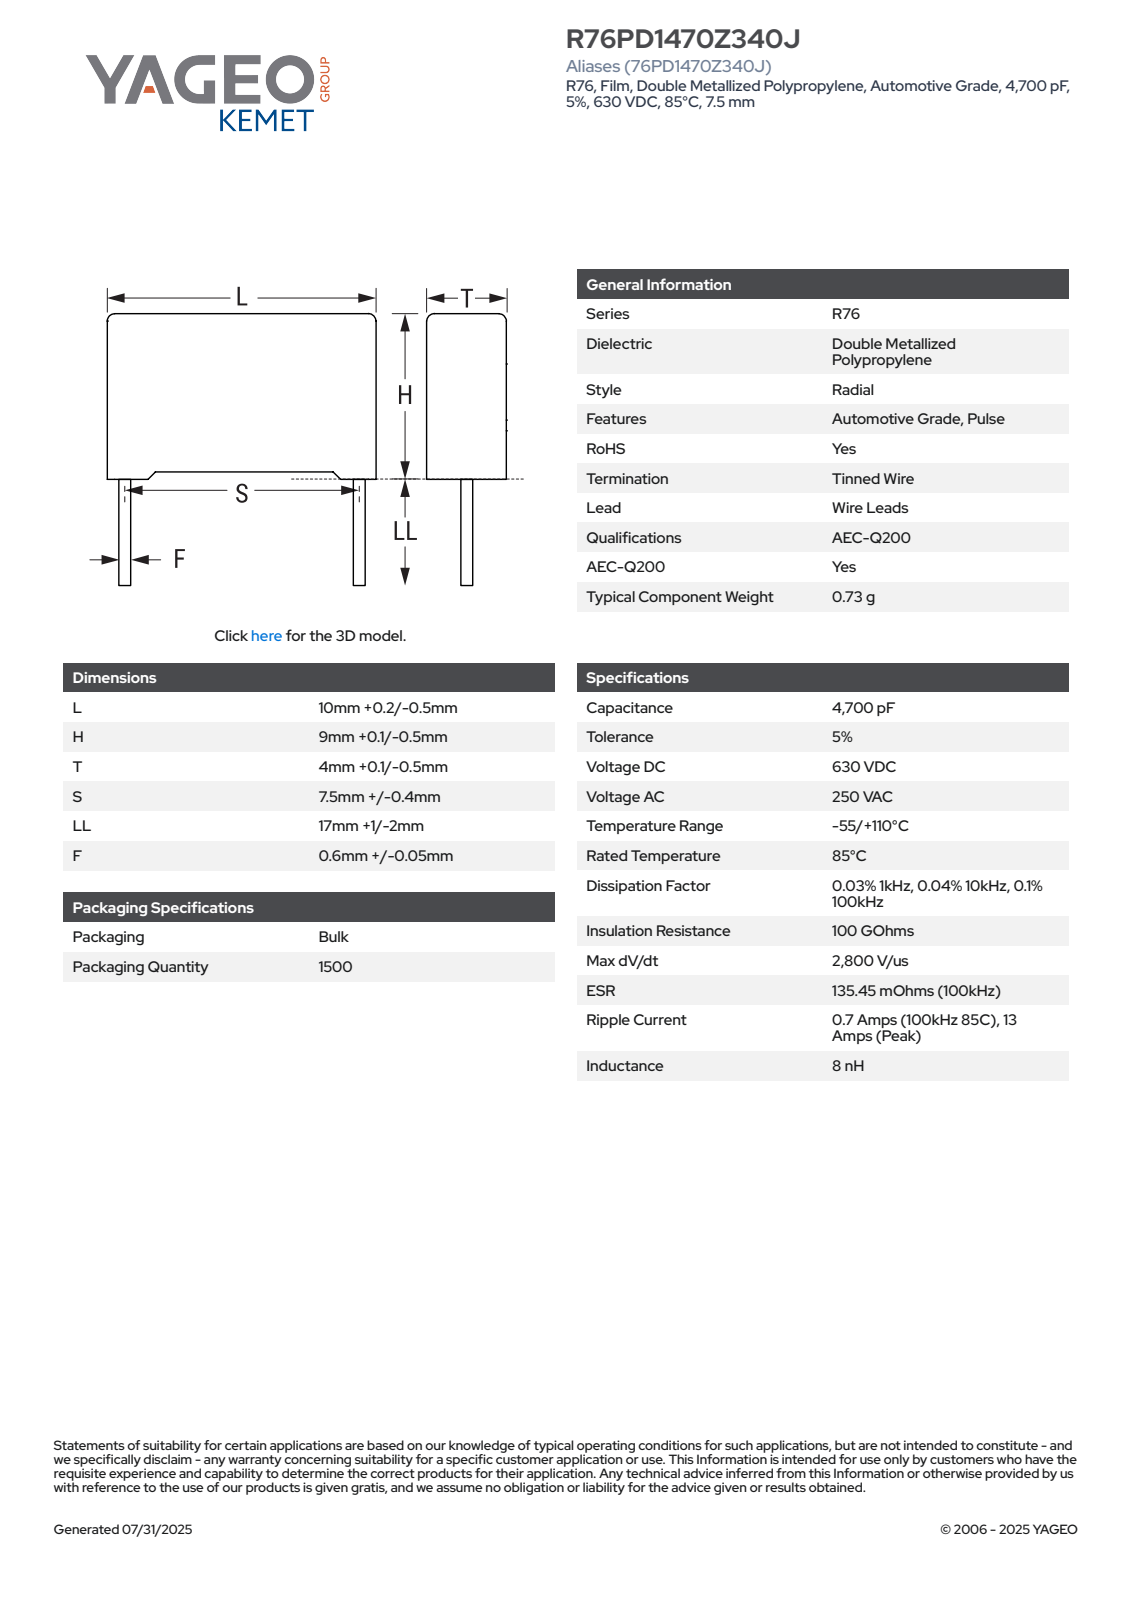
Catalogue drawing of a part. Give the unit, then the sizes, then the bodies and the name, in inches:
Units: inches
Overall size (bounding box): 1.067 × 0.402 × 0.162
Round bosses / shafts (diameter × count): ⌀0.026 ×2
Partial cylindrical surfaces — rounded edges, fillets, slot ends (radius × count): R0.02 ×4
Main face-to-face distances: 0.161, 0.402, 0.329, 0.013, 0.148, 0.03, 0.358, 0.135, 0.388, 0.012
Volume: 0.022 in³ · Surface area: 0.676 in²
Bodies: 4 solids, 85 faces (77 planar, 8 cylindrical, 0 other)
Part name (STEP PRODUCT): CFR_RB2_10X9X4_L10.2H9.1T4.1S7.5LL18F0.65
STEP written by: SolidWorks 2021 (AUTOMOTIVE_DESIGN)
